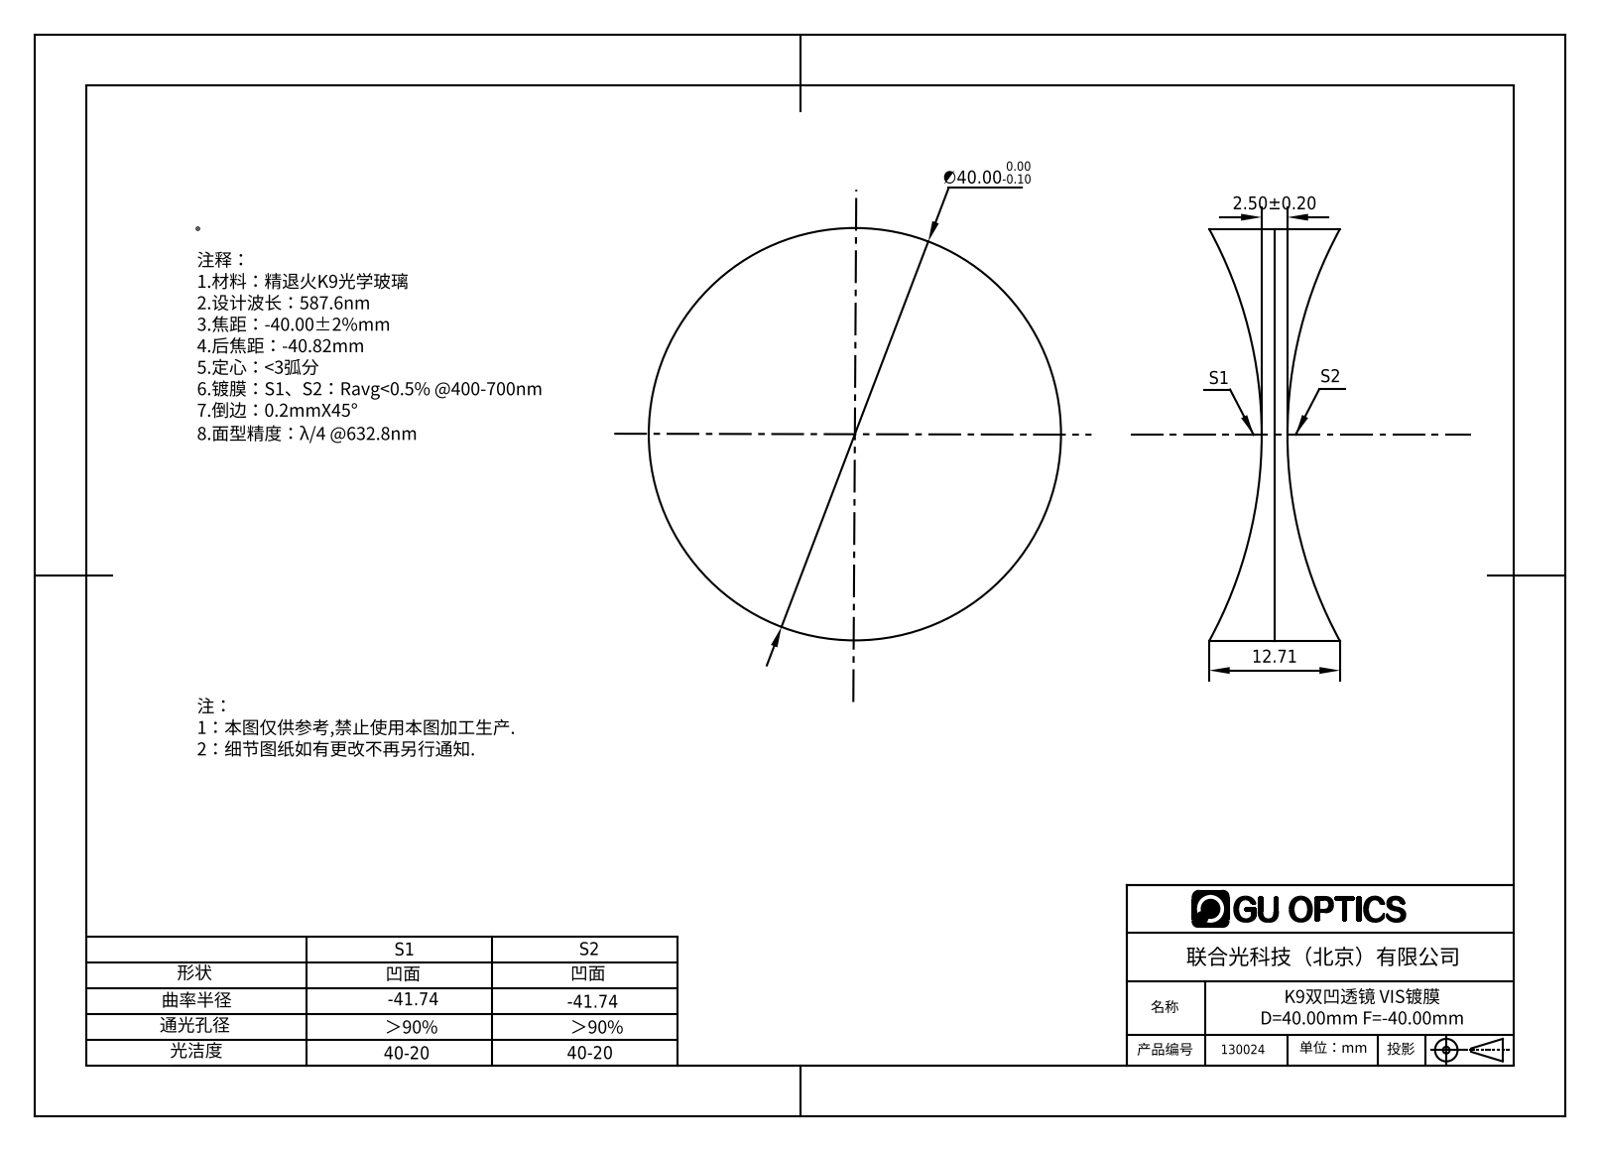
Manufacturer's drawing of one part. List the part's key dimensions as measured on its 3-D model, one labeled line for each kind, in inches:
Part name (STEP PRODUCT): 130011
STEP written by: SolidWorks 2016 (AUTOMOTIVE_DESIGN)
Units: inches
Bodies: 1 solid, 6 faces (0 planar, 2 cylindrical, 4 other)
Overall size (bounding box): 1.575 × 1.575 × 0.5
Volume: 0.575 in³ · Surface area: 6.625 in²
Round bosses / shafts (diameter × count): ⌀1.575 ×1
